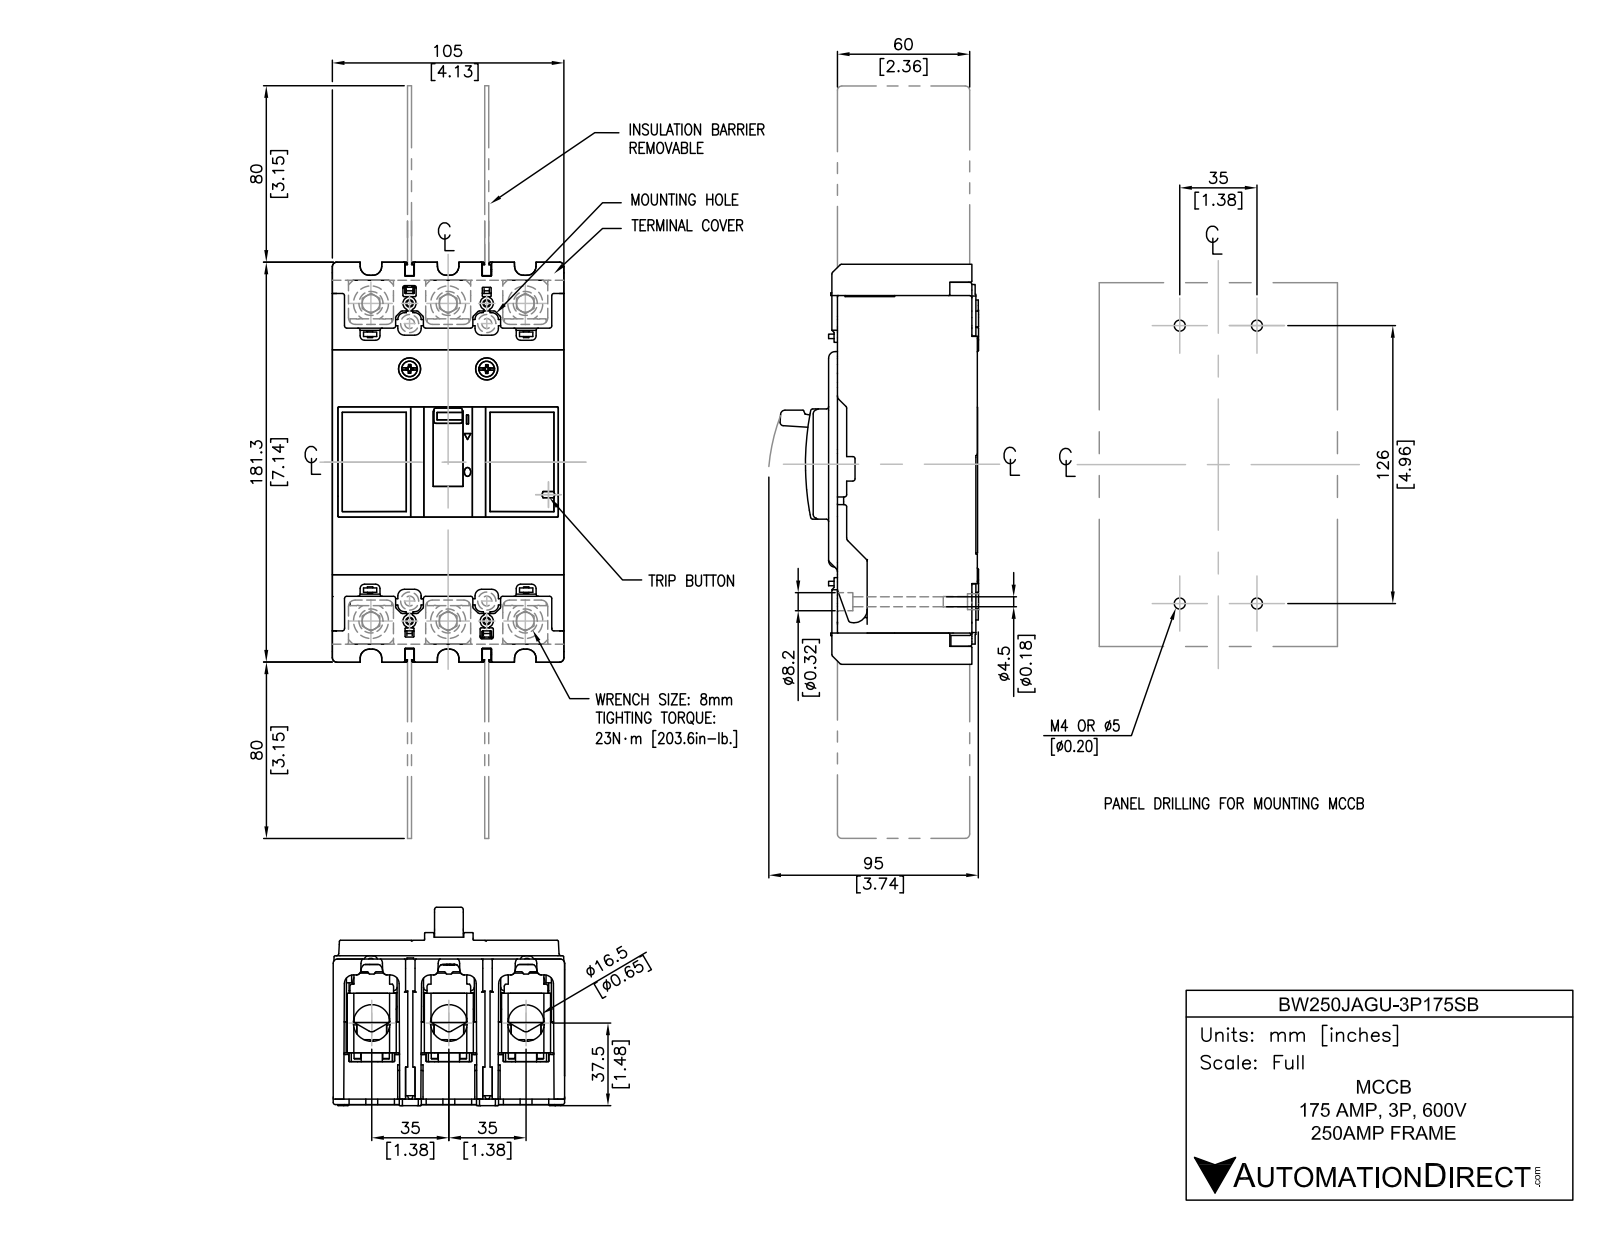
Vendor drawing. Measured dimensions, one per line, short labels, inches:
name: BW250JAGU-3P175SB
written by: SolidWorks 2018 (AUTOMOTIVE_DESIGN)
unit: in
bodies: 10 solids, 471 faces (338 planar, 121 cylindrical, 12 other)
size: 7.441 × 4.134 × 3.583
volume: 67.56 in³; area: 224 in²
holes: 6× ⌀0.315, 4× ⌀0.177, 4× ⌀0.323
bosses: 6× ⌀0.512
rounds: 36× R0.039, 16× R0.118, 8× R0.079, 3× R0.492
face distances: 0.098, 2.5, 4.134, 1.378, 0.787, 2.598, 1.24, 0.335, 0.157, 0.059
hole spacings: 0.775, 5.359, 1.378, 2.097, 5.703, 5.834, 5.669, 2.756
